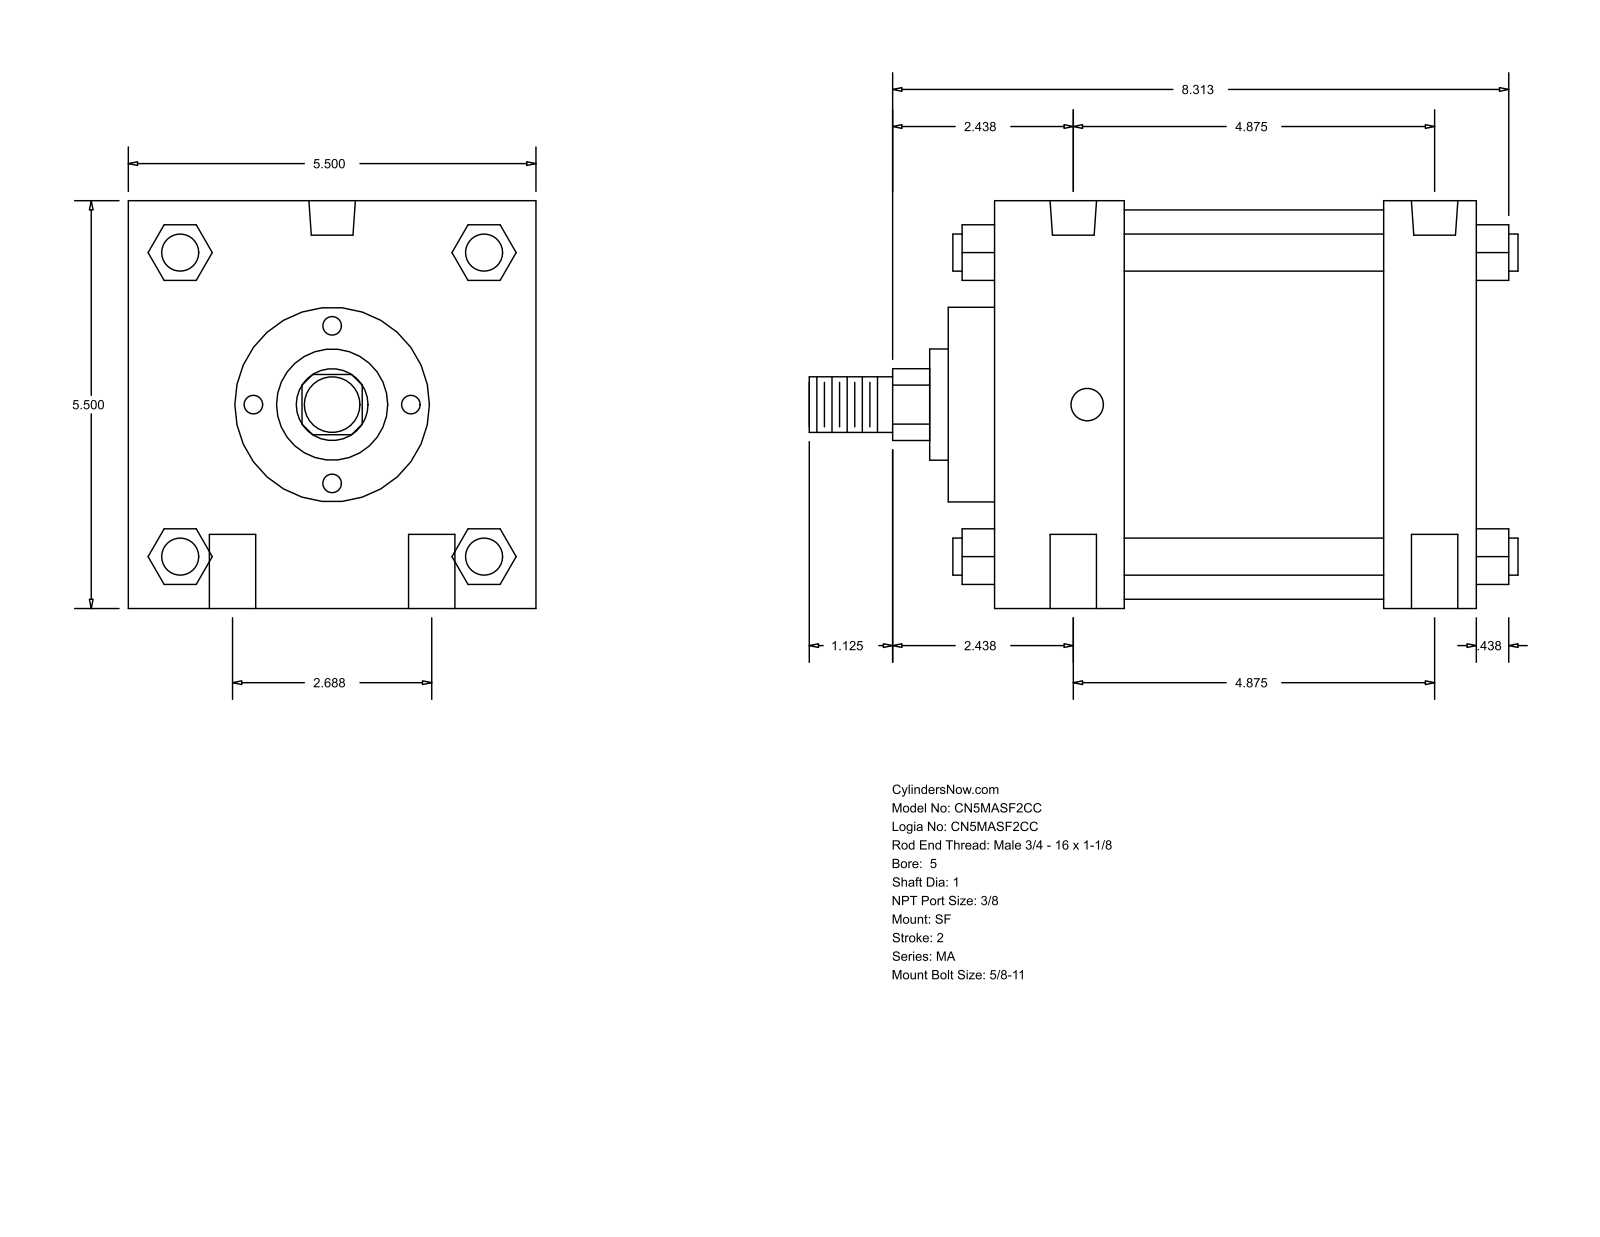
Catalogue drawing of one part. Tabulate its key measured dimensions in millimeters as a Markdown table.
| quantity | value |
| --- | --- |
| part name | MA_SF__0500_1 |
| STEP written by | GSSL Pune (CONFIG_CONTROL_DESIGN) |
| units | millimeters |
| bodies | 0 solids, 126 faces (95 planar, 31 cylindrical, 0 other) |
| overall size | 242.89 × 139.7 × 139.7 |
| round holes (diameter × count) | 15.88 × 4, 11.11 × 2, 15.93 × 2 |
| round bosses / shafts (diameter × count) | 12.7 × 4, 133.35 × 1, 66.67 × 1, 38.1 × 1, 25.4 × 1, 19.05 × 1 |
| partial cylindrical surfaces (radius × count) | 12.29 × 1 |
| main face-to-face distances | 139.7, 165.11, 44.46, 133.36, 88.9, 120.65, 31.75, 15.87, 60.33, 149.23 |
| hole center spacings | 34.13, 128.45, 123.83, 68.26, 141.4, 114.3 |
